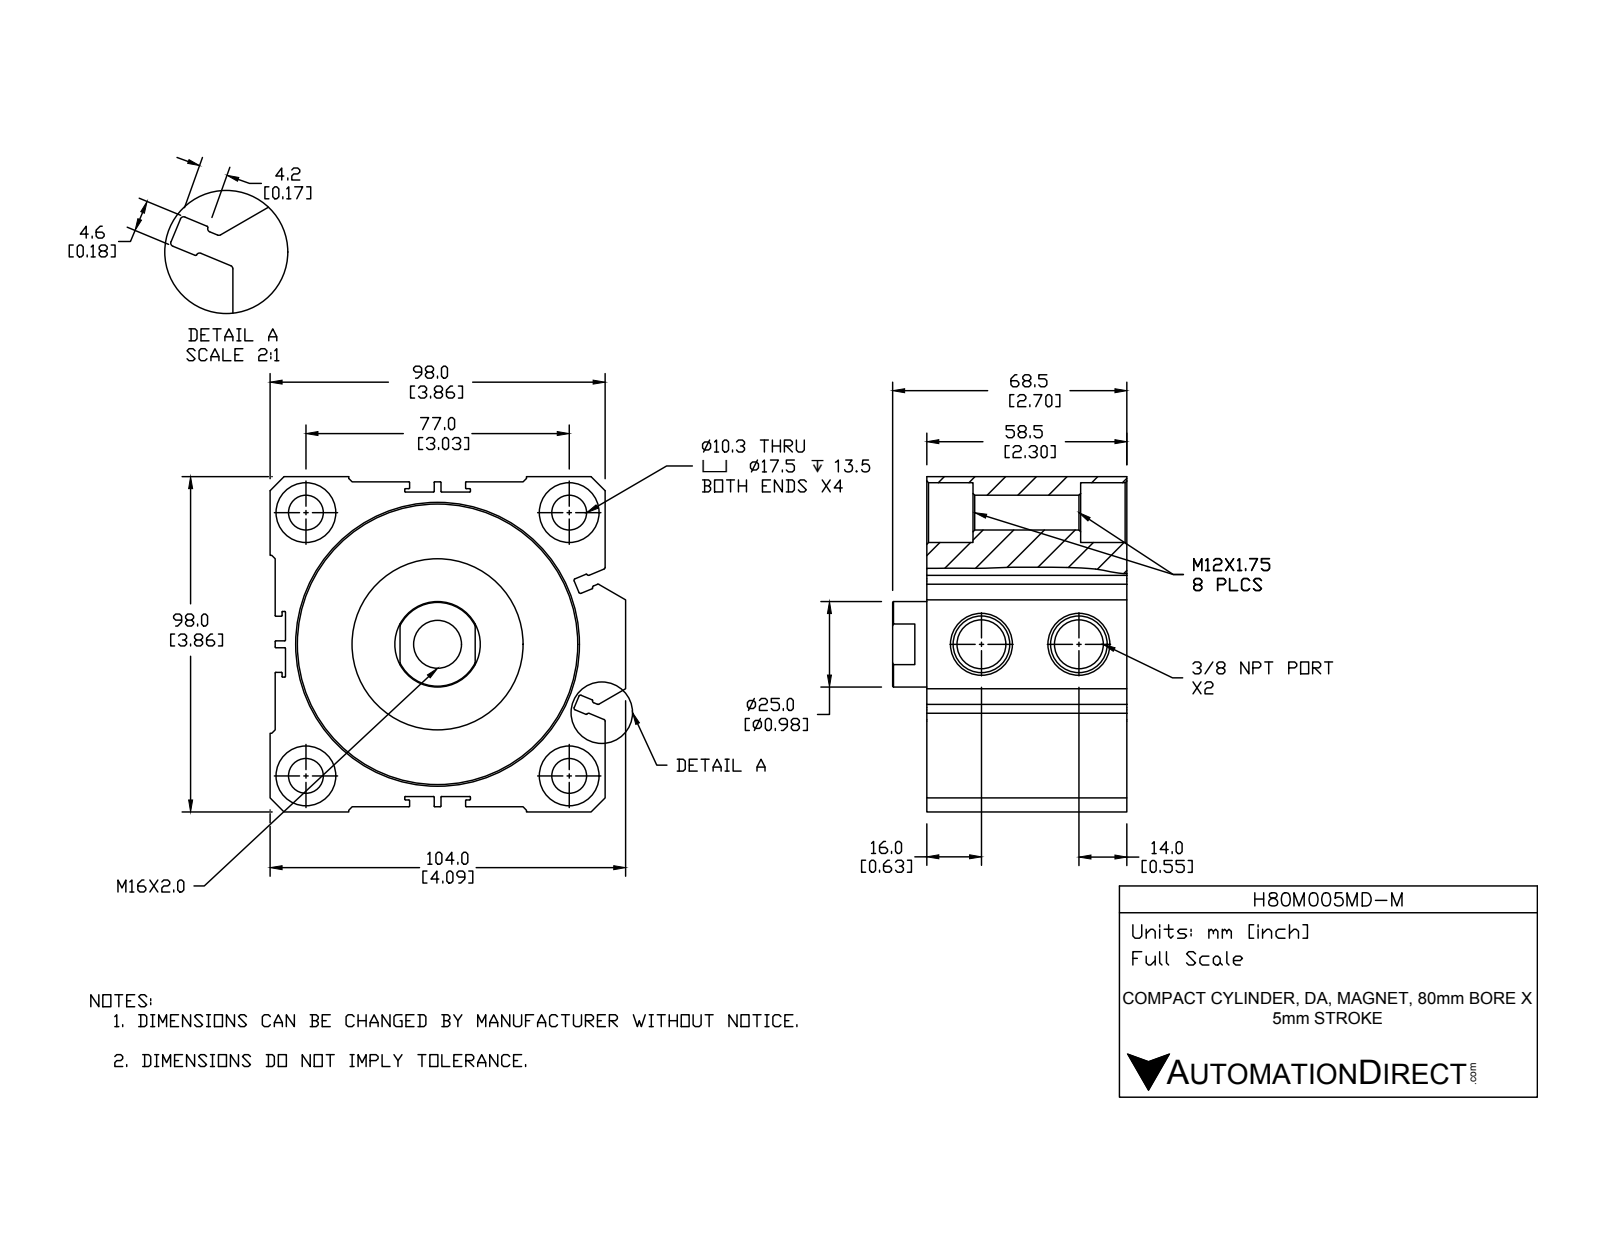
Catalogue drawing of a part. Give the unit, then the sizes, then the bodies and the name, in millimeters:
Units: millimetres
Overall size (bounding box): 104 × 98 × 68.5
Round holes (diameter × count): ⌀10.2 ×4, ⌀17.5 ×4, ⌀14.27 ×2, ⌀14 ×1, ⌀25 ×1, ⌀45.51 ×1, ⌀80 ×1, ⌀82 ×1
Round bosses / shafts (diameter × count): ⌀50 ×1, ⌀39 ×1
Partial cylindrical surfaces — rounded edges, fillets, slot ends (radius × count): R0.2 ×40, R0.5 ×12
Main face-to-face distances: 1.5, 96.5, 9, 36.1, 27.1, 41.1, 32.1, 5, 98, 10
Hole centre spacings: 54.45, 77, 108.89, 28.5
Volume: 448 894 mm³ · Surface area: 98 781 mm²
Bodies: 2 solids, 261 faces (105 planar, 103 cylindrical, 53 other)
Part name (STEP PRODUCT): H80M005MD-M-BODY; H80M005MD-M; H80M005MD-M-PISTON
STEP written by: SolidWorks 2015 (CONFIG_CONTROL_DESIGN)
